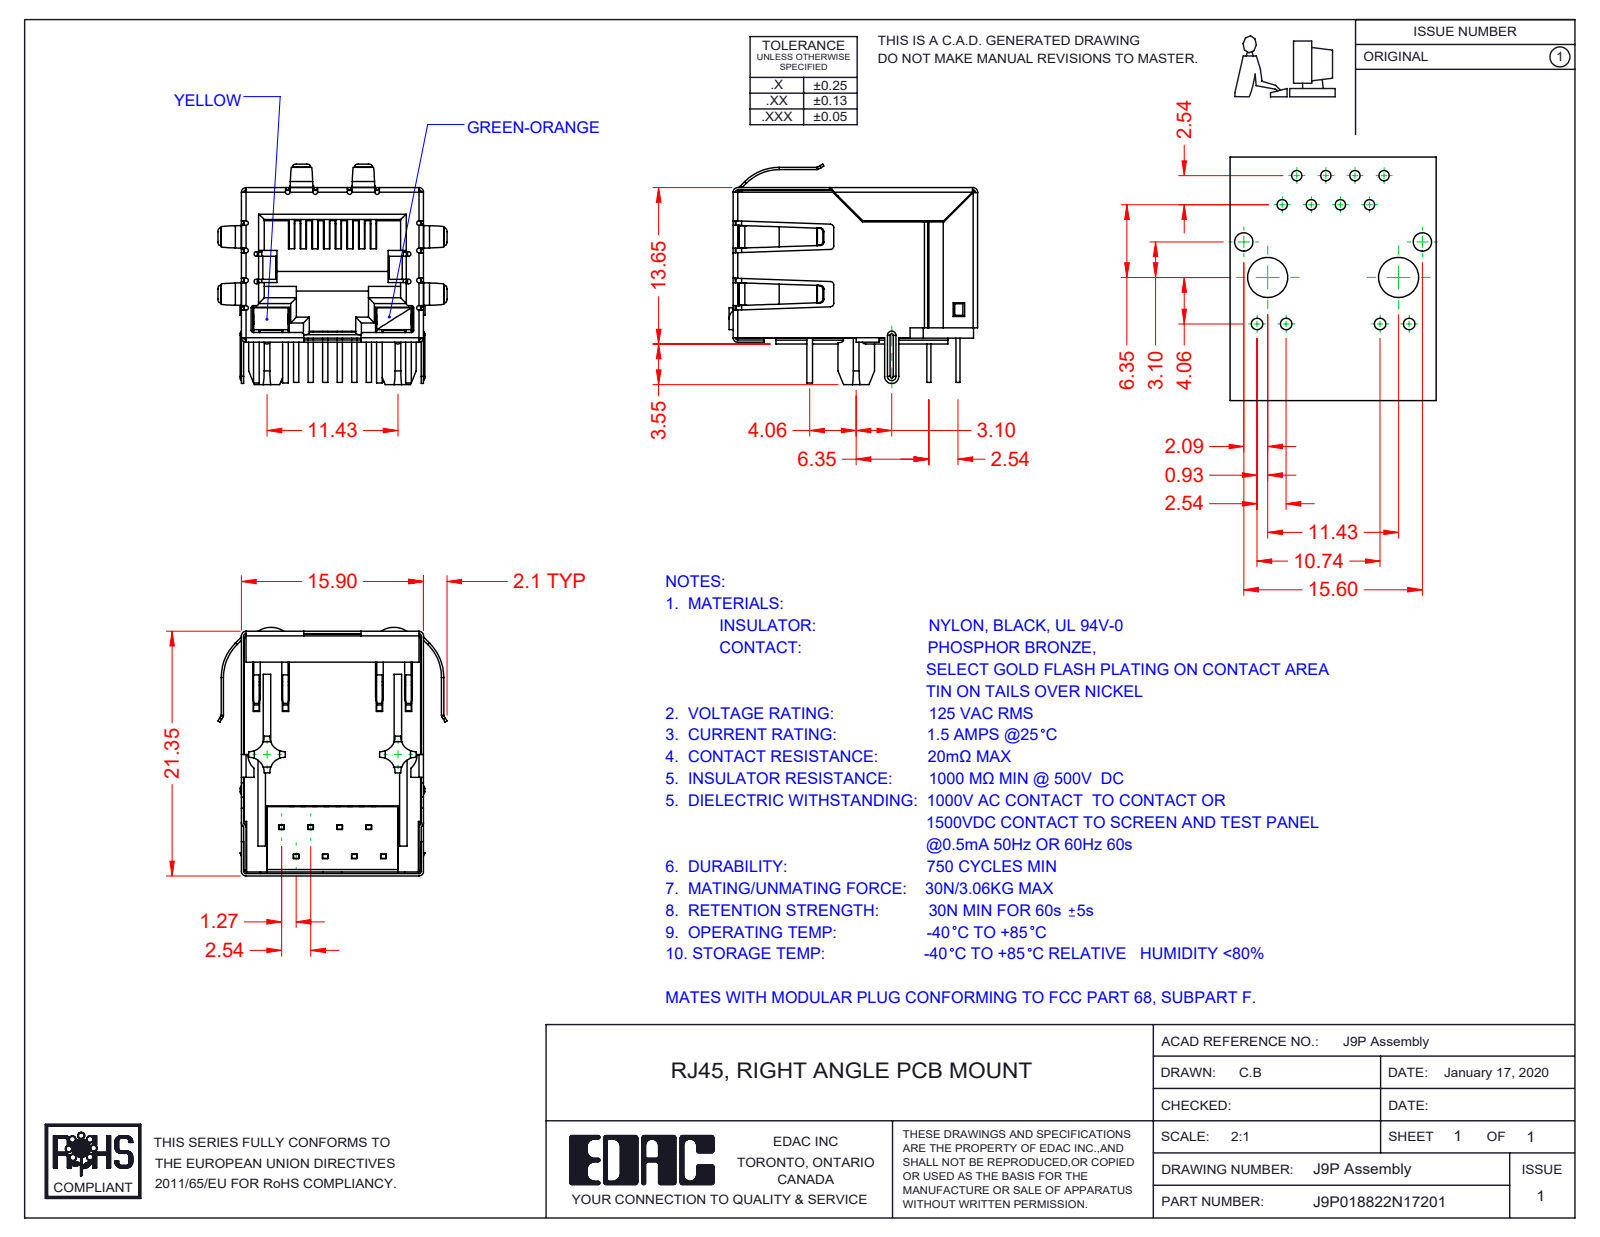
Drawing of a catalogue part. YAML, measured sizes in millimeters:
part_name: "9P-LED Insulator; 9P-LED LED LH_1-Yellow; 9P-LED Shield; J9P018822N17202 (+4 more)"
step_written_by: "SolidWorks 2016 (CONFIG_CONTROL_DESIGN)"
units: millimeters
bodies: {solids: 13, faces: 1474, planar: 1042, cylindrical: 338, other: 94}
overall_size: [21.7, 20, 19.25]
volume: 2687
surface_area: 7515
partial_cylinders:
  - {radius: 0.2, count: 39}
  - {radius: 0.5, count: 22}
  - {radius: 0.3, count: 20}
  - {radius: 0.4, count: 16}
  - {radius: 1.3, count: 8}
  - {radius: 0.23, count: 5}
  - {radius: 0.11, count: 4}
  - {radius: 0.31, count: 4}
face_to_face_distances: [15.45, 15.7, 15.65, 0.35, 0.54, 15.5, 12.36, 0.6, 1.4, 0.59]
